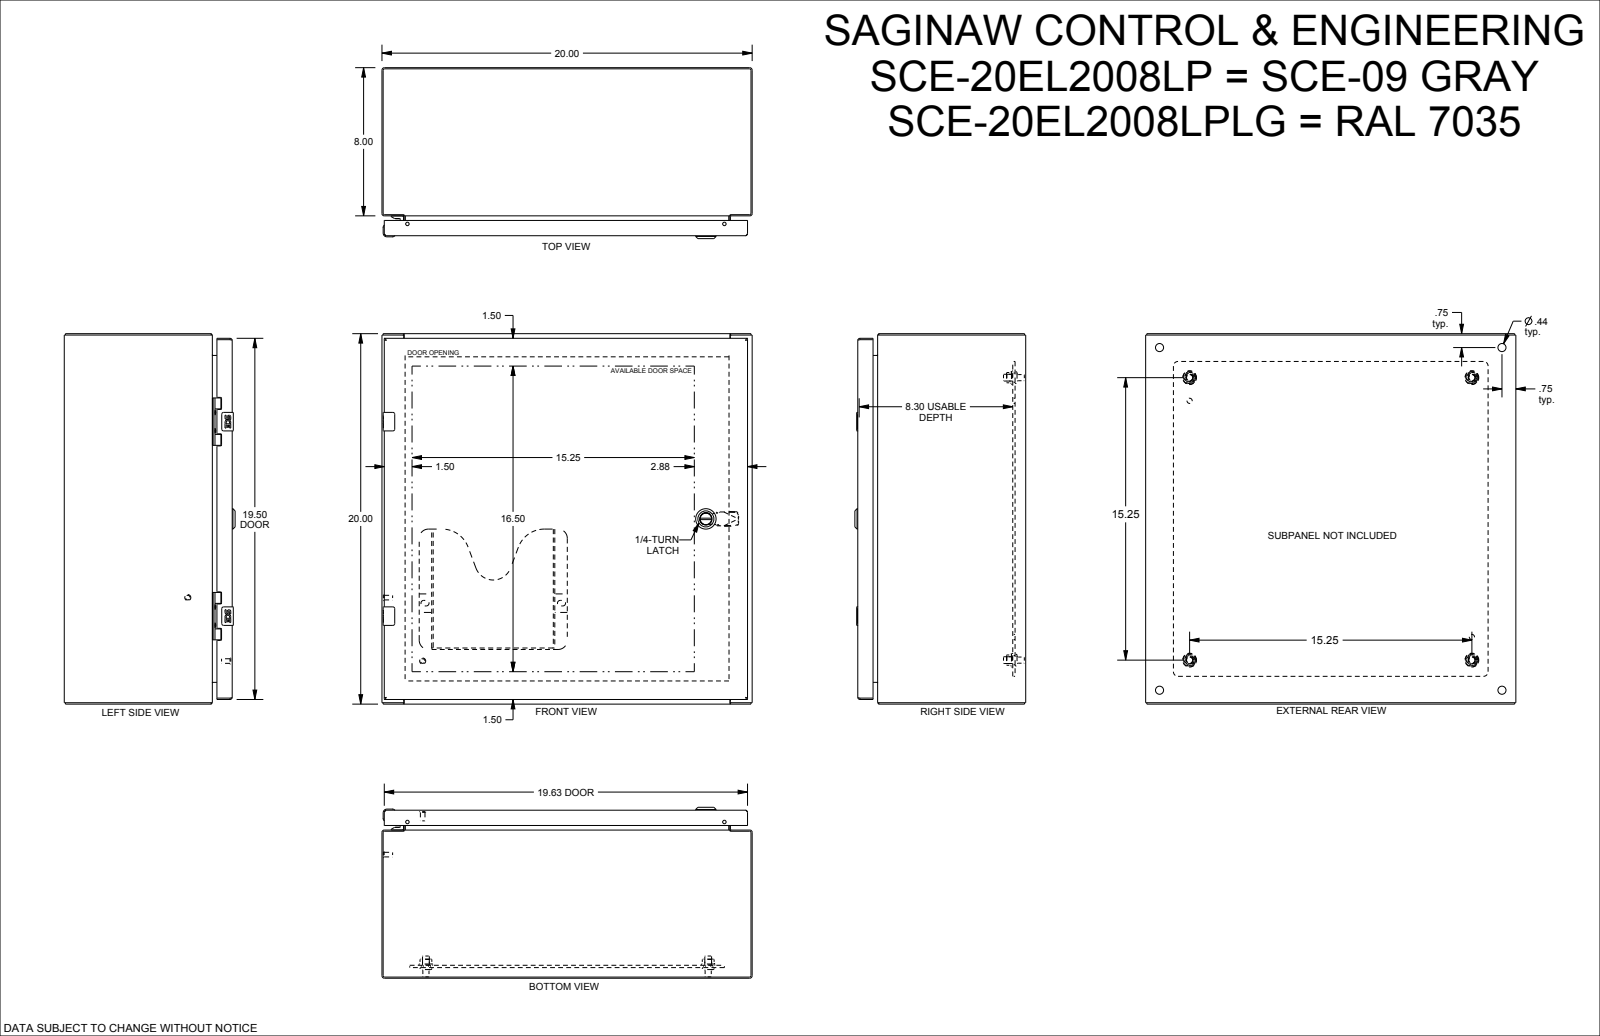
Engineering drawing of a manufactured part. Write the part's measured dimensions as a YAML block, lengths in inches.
part_name: "SCE-20EL2008LP"
step_written_by: "SolidWorks 2021 (AUTOMOTIVE_DESIGN)"
units: inches
bodies: {solids: 41, faces: 2404, planar: 918, cylindrical: 694, other: 792}
overall_size: [20, 20, 9.23]
volume: 169.6
surface_area: 4131
round_holes:
  - {diameter: 0.172, count: 4}
  - {diameter: 0.205, count: 4}
  - {diameter: 0.244, count: 4}
  - {diameter: 0.266, count: 4}
  - {diameter: 0.367, count: 4}
  - {diameter: 0.375, count: 4}
  - {diameter: 0.437, count: 4}
  - {diameter: 0.5, count: 4}
  - {diameter: 0.04, count: 2}
  - {diameter: 0.188, count: 2}
  - {diameter: 0.218, count: 2}
  - {diameter: 0.25, count: 2}
round_bosses_or_shafts:
  - {diameter: 0.17, count: 6}
  - {diameter: 0.366, count: 4}
  - {diameter: 0.332, count: 4}
  - {diameter: 0.25, count: 4}
  - {diameter: 0.248, count: 4}
  - {diameter: 0.24, count: 4}
  - {diameter: 0.196, count: 3}
  - {diameter: 0.563, count: 2}
partial_cylinders:
  - {radius: 0.012, count: 30}
  - {radius: 0.01, count: 28}
  - {radius: 0.015, count: 24}
  - {radius: 0.04, count: 17}
  - {radius: 0.06, count: 13}
  - {radius: 0.02, count: 12}
  - {radius: 0.029, count: 12}
  - {radius: 0.1, count: 12}
face_to_face_distances: [0.075, 19.925, 0.06, 9.073, 8.998, 9.013, 8.938, 19.85, 20, 0.125]
hole_center_spacings: [16.953, 0.985, 10.5, 0.02, 0.493, 0.494, 2.298, 4.493]
